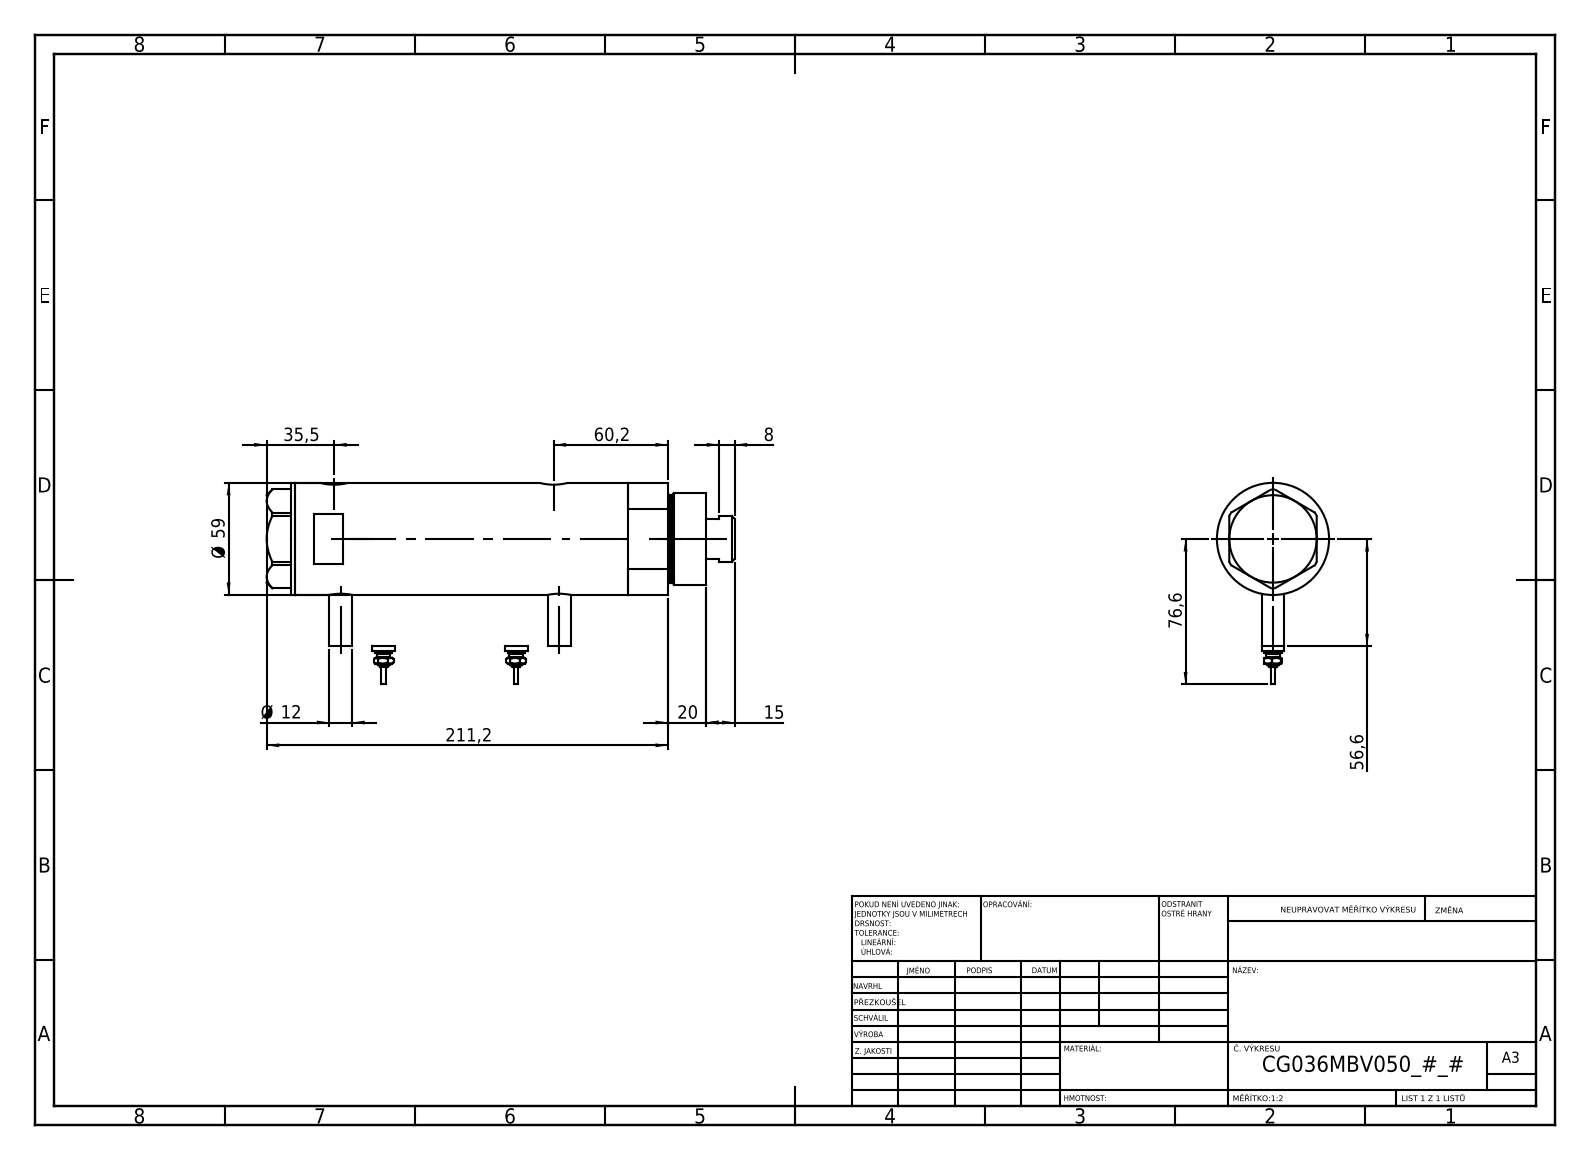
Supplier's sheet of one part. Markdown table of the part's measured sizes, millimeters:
| quantity | value |
| --- | --- |
| part name | V270CG_BACK; V270CG_VC; V270CG_MIDDLE; Switch (+1 more) |
| STEP written by | SolidWorks 2019 (CONFIG_CONTROL_DESIGN) |
| units | millimeters |
| bodies | 6 solids, 212 faces (79 planar, 69 cylindrical, 64 other) |
| overall size | 246.2 × 106.1 × 59 |
| volume | 580 147 mm³ |
| surface area | 117 158 mm² |
| round holes (diameter × count) | 9.73 × 2, 12.5 × 2, 15 × 2, 8.5 × 1, 25 × 1, 26.5 × 1, 36 × 1, 40 × 1, 52 × 1 |
| round bosses / shafts (diameter × count) | 12 × 4, 9 × 2, 7 × 2, 4.5 × 2, 2.5 × 2, 59 × 1, 48 × 1, 46 × 1 |
| main face-to-face distances | 137.2, 23.5, 113.7, 15, 38.5, 152.2, 2, 231.2, 216.2, 50 |
| hole center spacings | 2.9, 3.5, 112, 114.9, 115.5, 118.4 |
